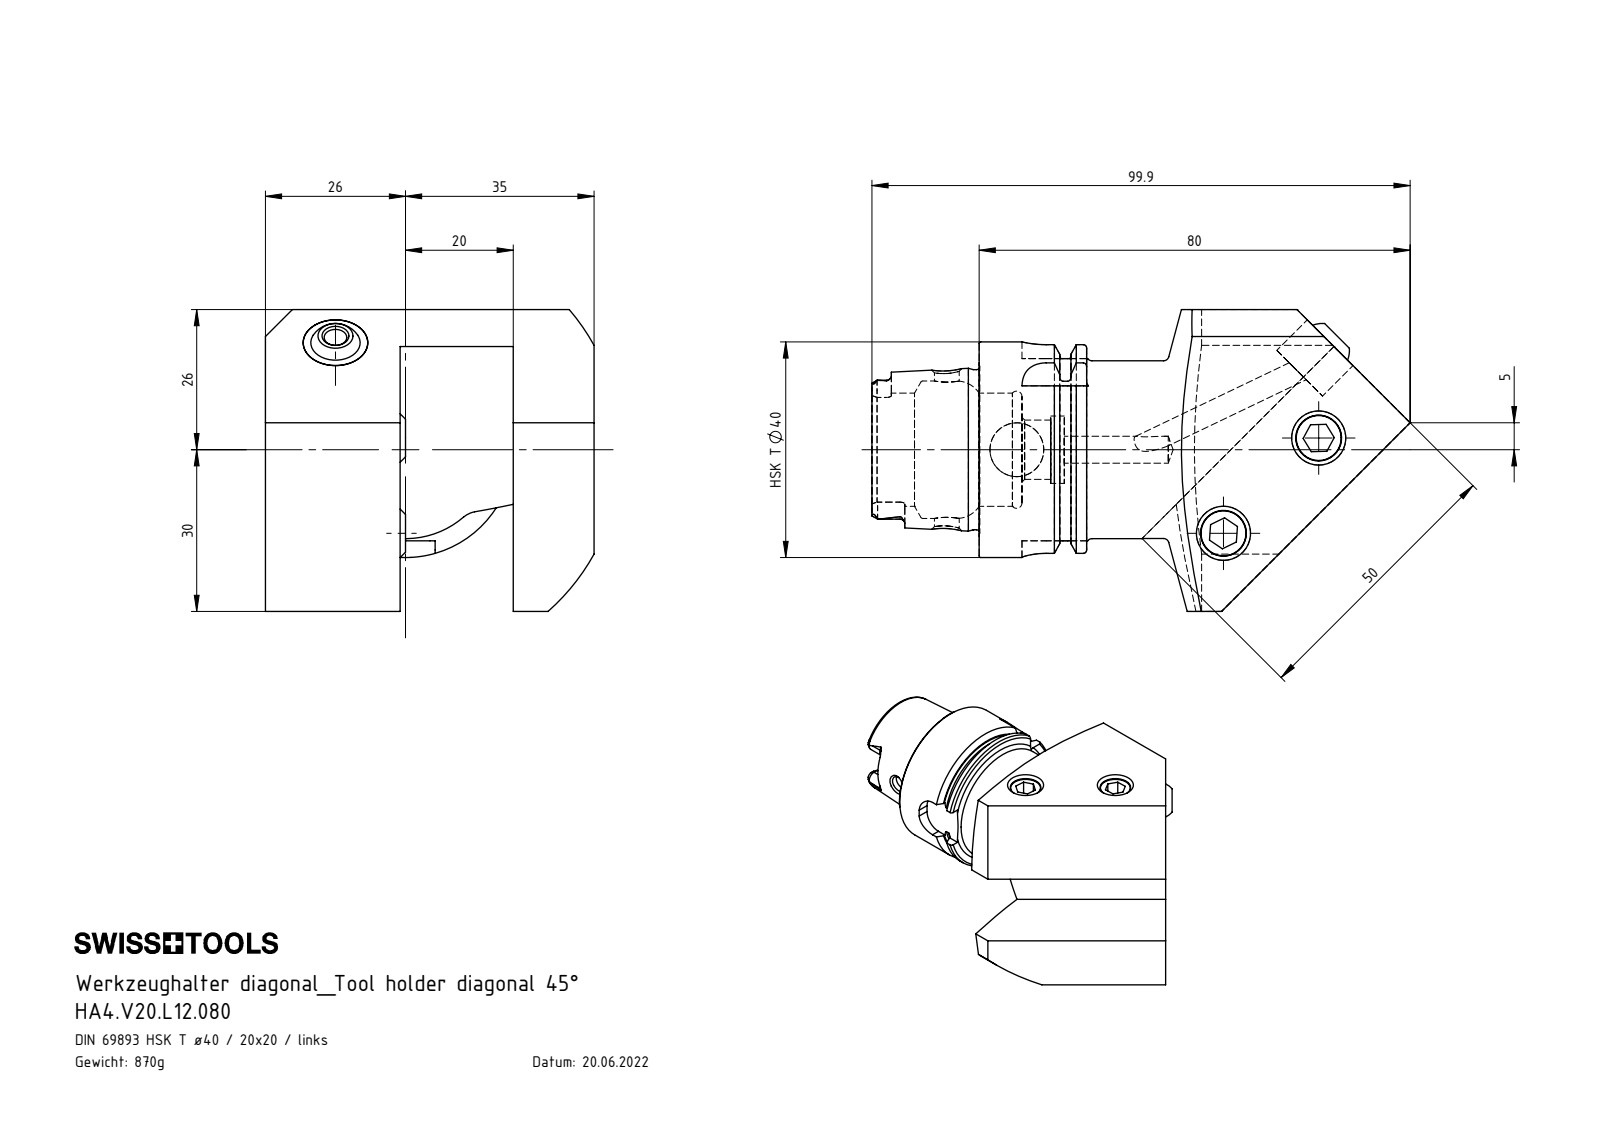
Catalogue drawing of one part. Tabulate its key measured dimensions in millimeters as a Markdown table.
| quantity | value |
| --- | --- |
| part name | KU1-U12.001.010; HA4-V20.L12.080_A; HA4.V20.L12.080; KU1-U12.001.010_2 (+2 more) |
| STEP written by | SolidWorks 2022 (CONFIG_CONTROL_DESIGN) |
| units | millimeters |
| bodies | 5 solids, 239 faces (79 planar, 67 cylindrical, 93 other) |
| overall size | 99.9 × 61 × 56 |
| volume | 111 148 mm³ |
| surface area | 27 799 mm² |
| round holes (diameter × count) | 4.2 × 2, 8.5 × 2, 4.6 × 1, 5 × 1, 7 × 1, 10 × 1, 11 × 1, 12 × 1, 12.5 × 1, 21 × 1, 25.5 × 1 |
| round bosses / shafts (diameter × count) | 10 × 2, 40 × 1, 34.75 × 1, 33 × 1, 29.71 × 1 |
| partial cylindrical surfaces (radius × count) | 0.9 × 6, 1.88 × 4, 4.5 × 4, 40 × 1 |
| main face-to-face distances | 61, 20, 15, 46, 25, 36, 21, 7.95, 8, 19.95 |
| hole center spacings | 25, 41.37, 56.07 |
